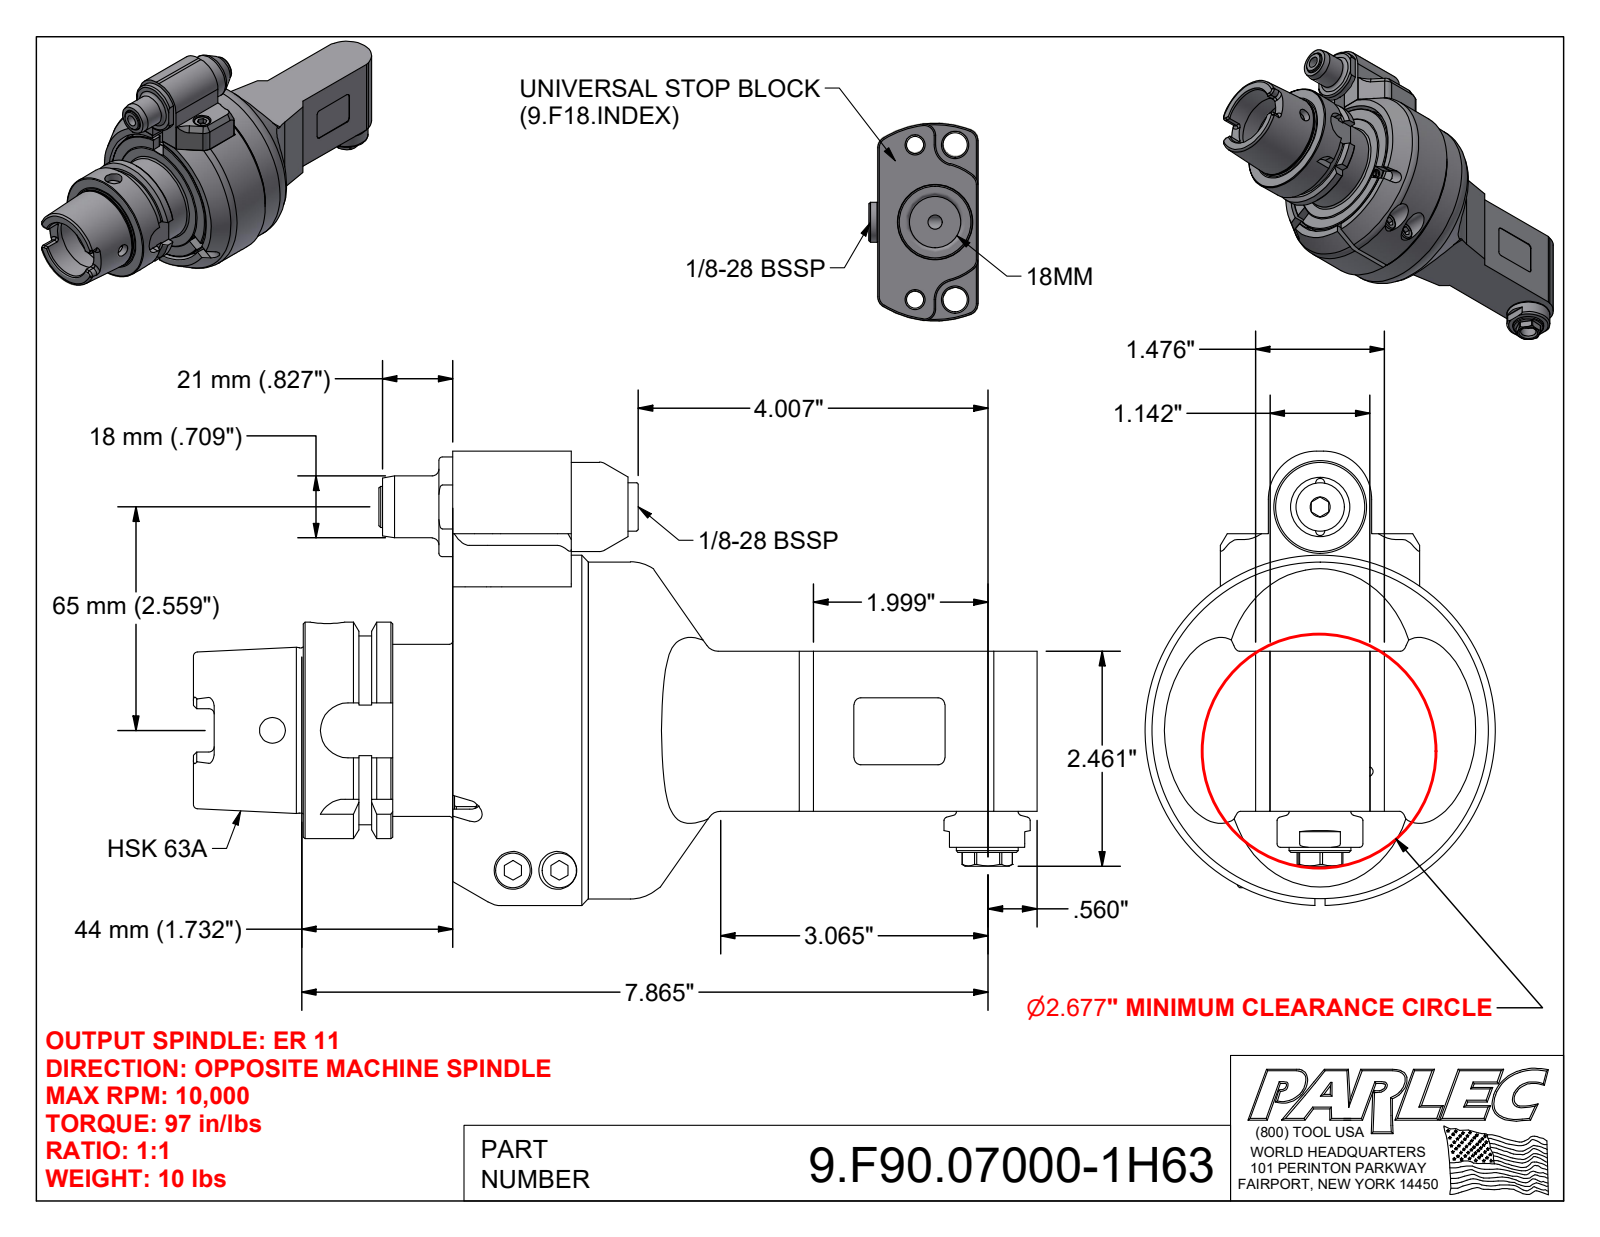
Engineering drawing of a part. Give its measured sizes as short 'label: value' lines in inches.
name: 9.F90.07000-1H63; 9_GA1_566_2 (Type 1, H63A 65mm); 9_F90_07000
written by: Autodesk Inventor 2022 (AUTOMOTIVE_DESIGN)
unit: in
bodies: 5 solids, 536 faces (253 planar, 147 cylindrical, 136 other)
size: 9.665 × 5.206 × 4.016
volume: 48.99 in³; area: 222.2 in²
holes: 21× ⌀0.335, 2× ⌀0.102, 2× ⌀0.165, 2× ⌀0.197, 2× ⌀0.295, 2× ⌀0.409, 2× ⌀0.433, 2× ⌀0.492, 1× ⌀0.098, 1× ⌀0.118, 1× ⌀0.256, 1× ⌀0.276
bosses: 4× ⌀0.394, 4× ⌀0.236, 3× ⌀0.709, 2× ⌀0.315, 2× ⌀0.098, 1× ⌀4.016, 1× ⌀3.858, 1× ⌀3.031
rounds: 12× R0.079, 6× R0.059, 4× R0.113, 4× R0.157, 4× R0.315, 2× R0.02, 2× R0.039, 2× R0.138
face distances: 1.26, 0.02, 1.024, 0.738, 1.831, 0.276, 1.555, 2.569, 1.142, 0.295
hole spacings: 1.516, 2.144, 1.824, 3.002, 0.835, 2.651, 2.914, 3.031
